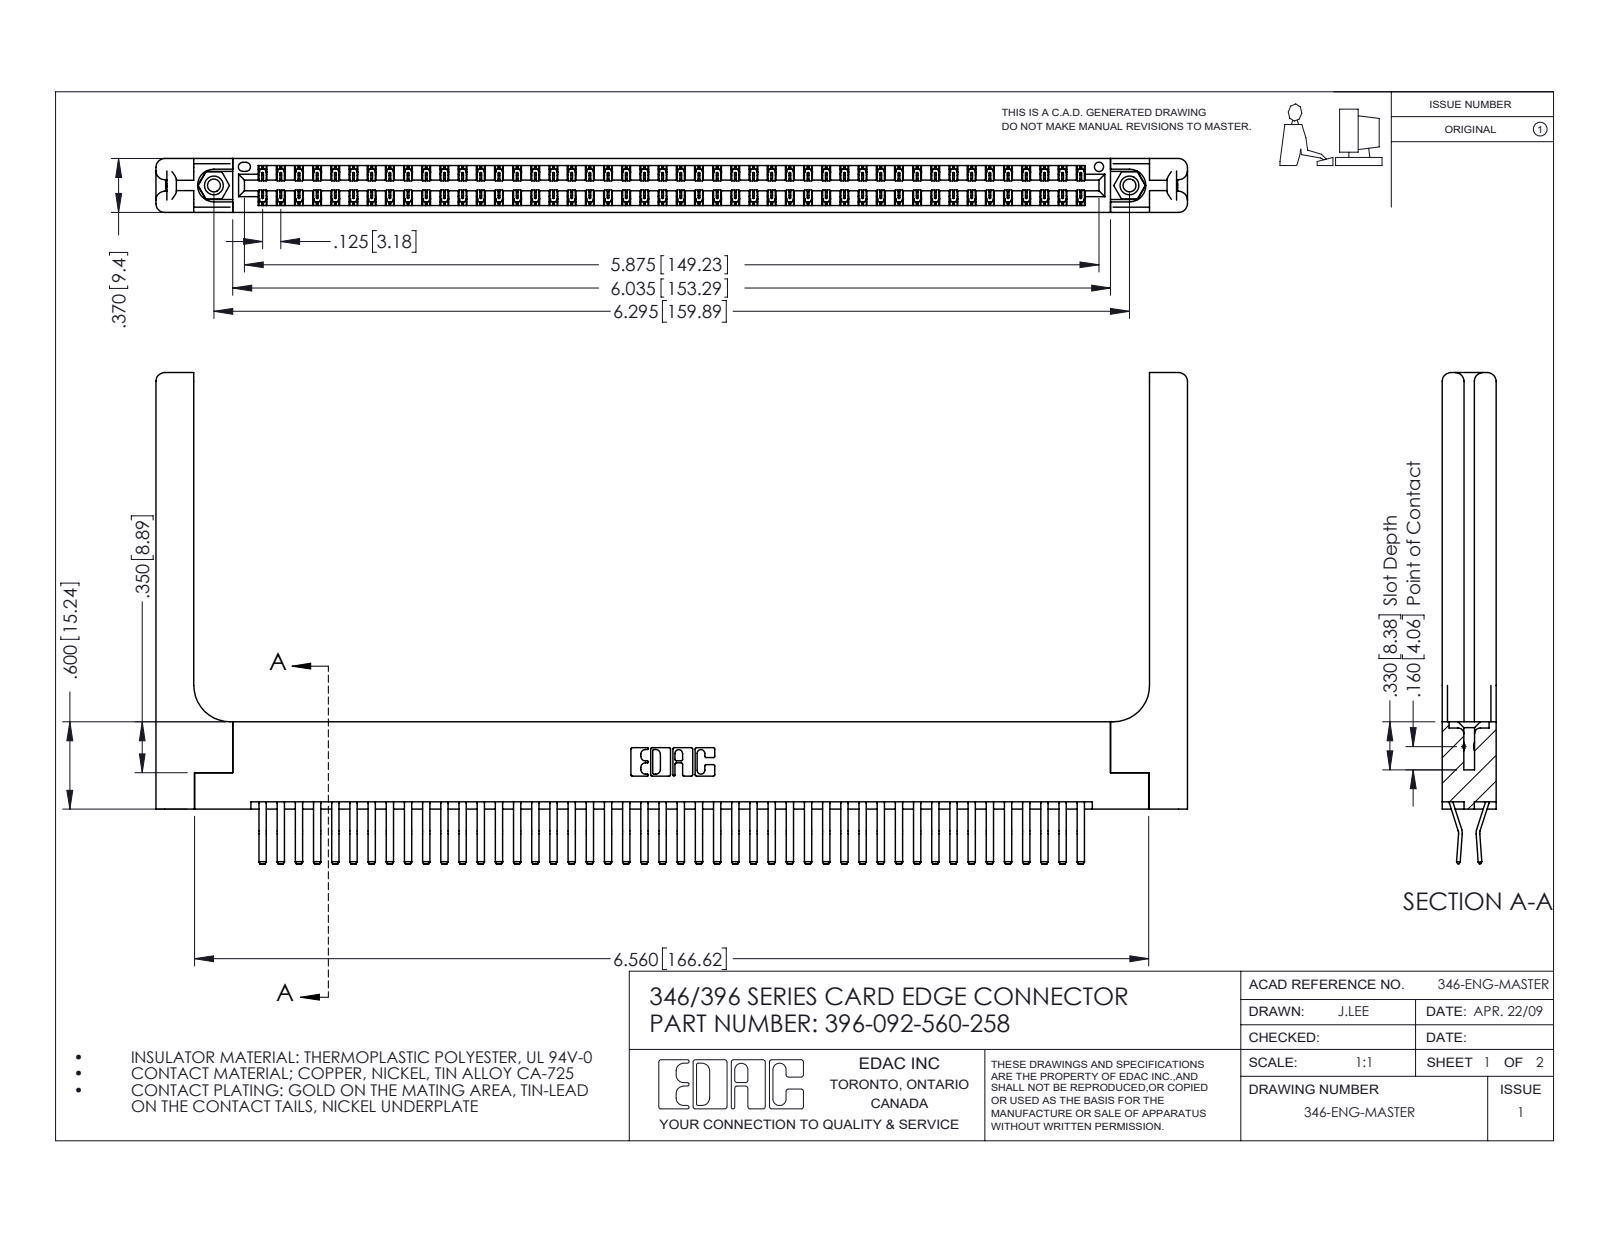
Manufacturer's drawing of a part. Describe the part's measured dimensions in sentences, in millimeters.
The part is named "346 Part_Flush Mounting Lugs - 0.156 Dia-TH; 345-292-001_560 Tail; 345-250-001_345-250-001-102; 396-092-560-258 (+1 more)". Its 3-D file was written by "SolidWorks 2016 (CONFIG_CONTROL_DESIGN)". It is 97 solids with 5346 faces: 3444 planar, 1842 cylindrical and 60 other. Overall it measures 180.1 by 85.7 by 9.4 millimeters. Its volume is 25 690 cubic millimeters and its surface area 31 660 square millimeters. Round holes: 2 of diameter 2.3, 2 of diameter 3.2, 2 of diameter 4, 1 of diameter 1.6. Round bosses or shafts: 2 of diameter 3.9. Partial cylindrical surfaces (rounded edges, fillets, slot ends): 138 of radius 0.2, 22 of radius 0.3, 16 of radius 1.5, 6 of radius 0.2, 6 of radius 0.8, 3 of radius 0.7, 2 of radius 0.3, 2 of radius 0.4. The main face-to-face distances are 9.4, 1.2, 8.2, 1.8, 0.6, 3.8, 3.8, 6.4, 7.6, 7. The hole center spacings are 6.2, 154.6, 159.9.
